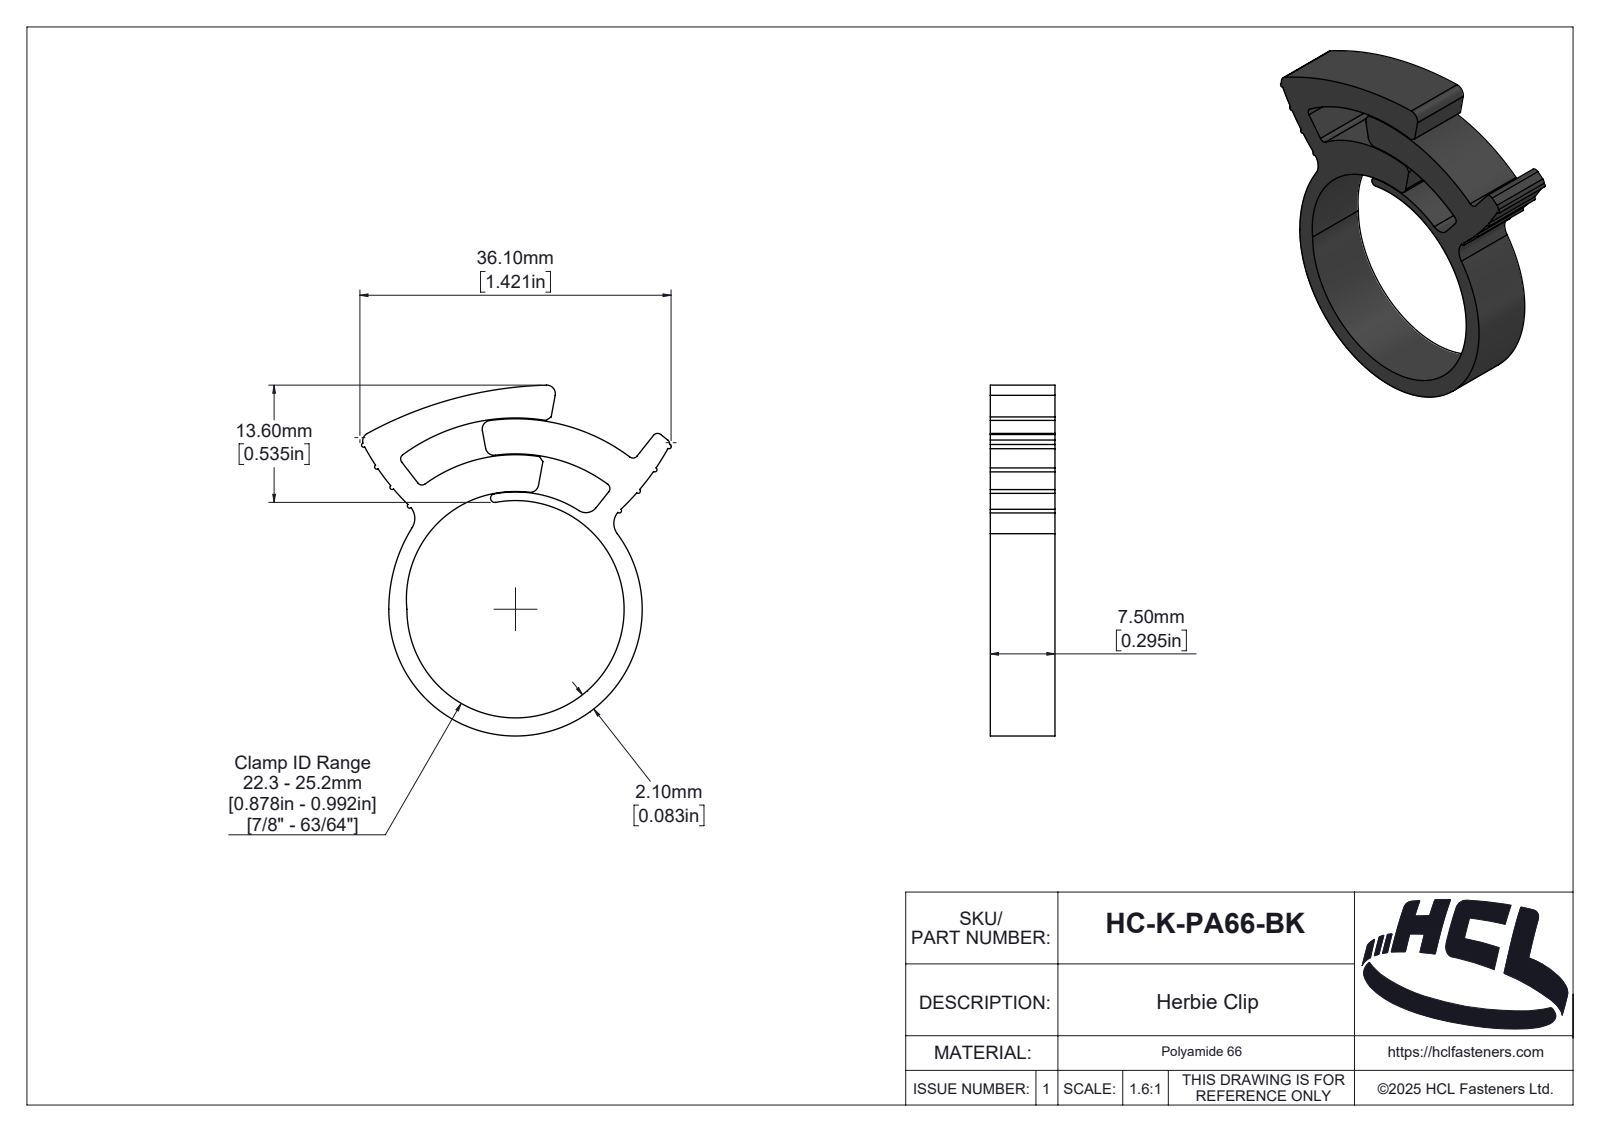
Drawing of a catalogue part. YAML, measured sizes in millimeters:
part_name: "HC-K-PA66-BK"
step_written_by: "SolidWorks 2025 (AUTOMOTIVE_DESIGN)"
units: millimeters
bodies: {solids: 1, faces: 162, planar: 13, cylindrical: 100, other: 49}
overall_size: [40.68, 35.92, 7.5]
volume: 3071
surface_area: 3120
partial_cylinders:
  - {radius: 0.25, count: 8}
  - {radius: 0.6, count: 6}
  - {radius: 1, count: 5}
  - {radius: 2, count: 2}
  - {radius: 0.17, count: 1}
  - {radius: 0.5, count: 1}
  - {radius: 0.67, count: 1}
  - {radius: 0.84, count: 1}
face_to_face_distances: [7.5]
